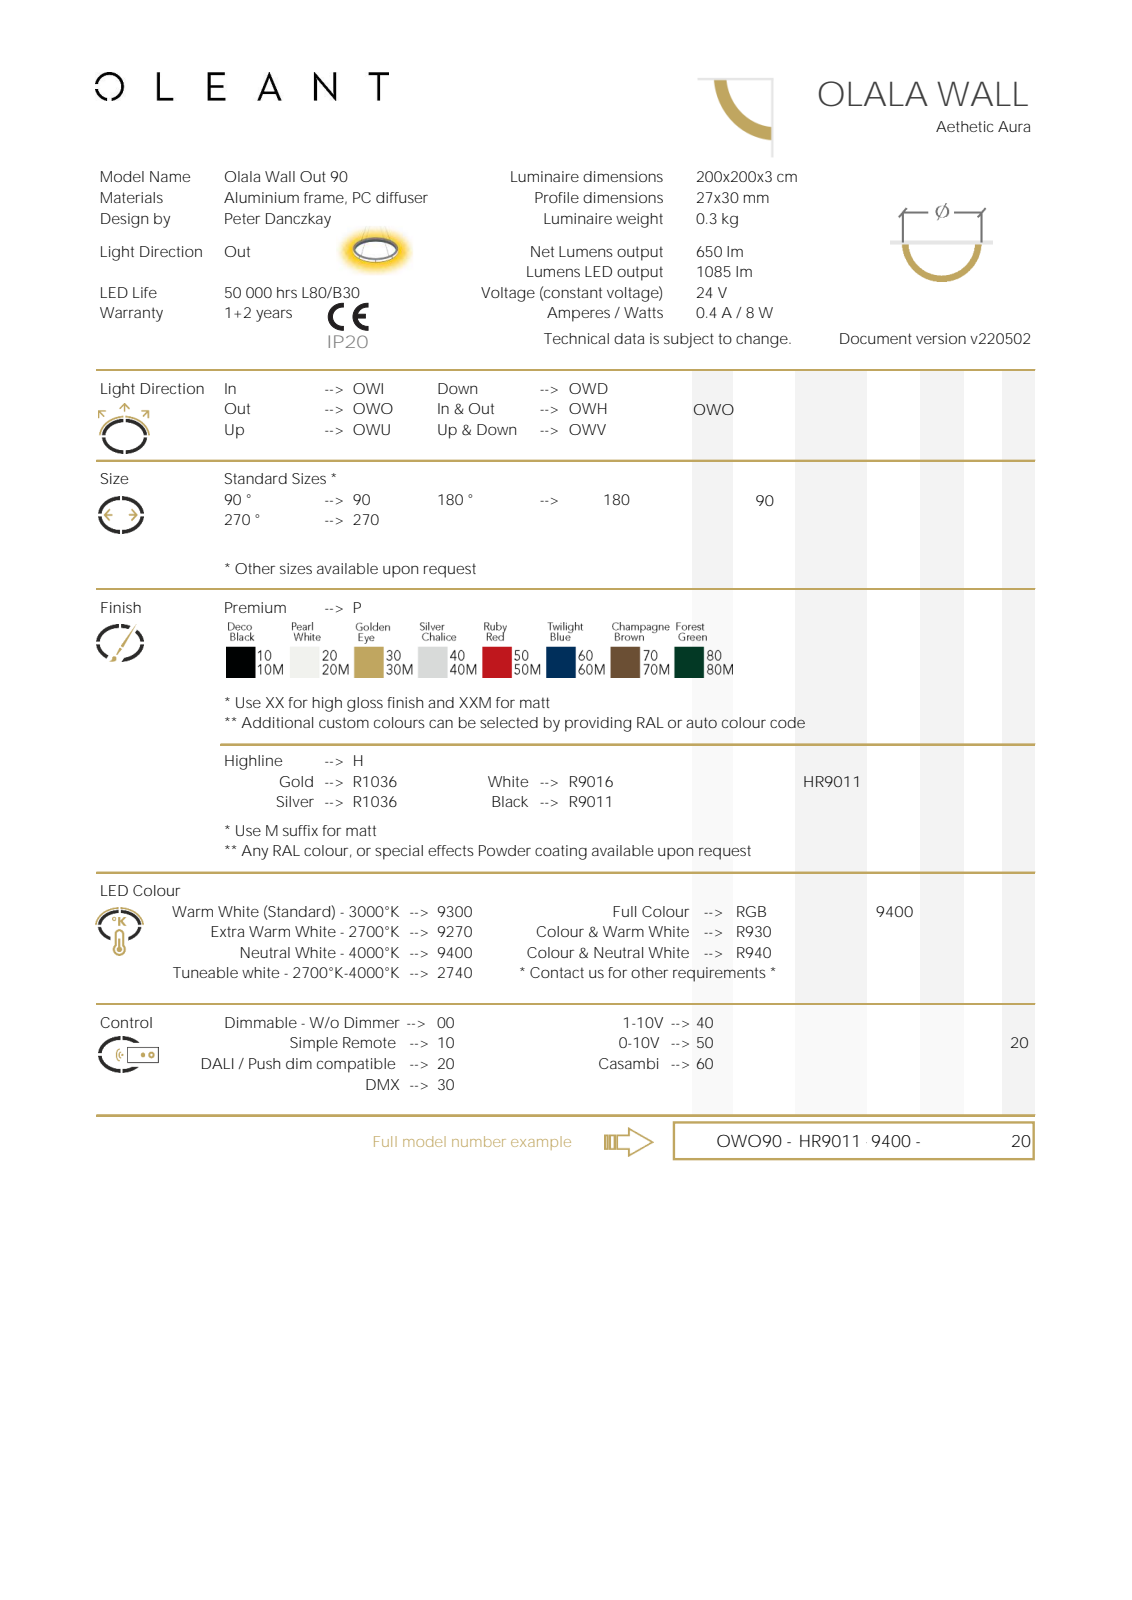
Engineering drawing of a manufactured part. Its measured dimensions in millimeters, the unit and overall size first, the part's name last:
Units: millimetres
Overall size (bounding box): 200 × 200 × 30
Partial cylindrical surfaces — rounded edges, fillets, slot ends (radius × count): R173.5 ×1, R175.5 ×1, R199 ×1, R200 ×1
Main face-to-face distances: 2, 28, 26, 30, 12
Volume: 247 865 mm³ · Surface area: 78 937 mm²
Bodies: 2 solids, 26 faces (16 planar, 6 cylindrical, 4 other)
Part name (STEP PRODUCT): olalawall; frame; plexi
STEP written by: Autodesk Inventor 2020 (AUTOMOTIVE_DESIGN)
